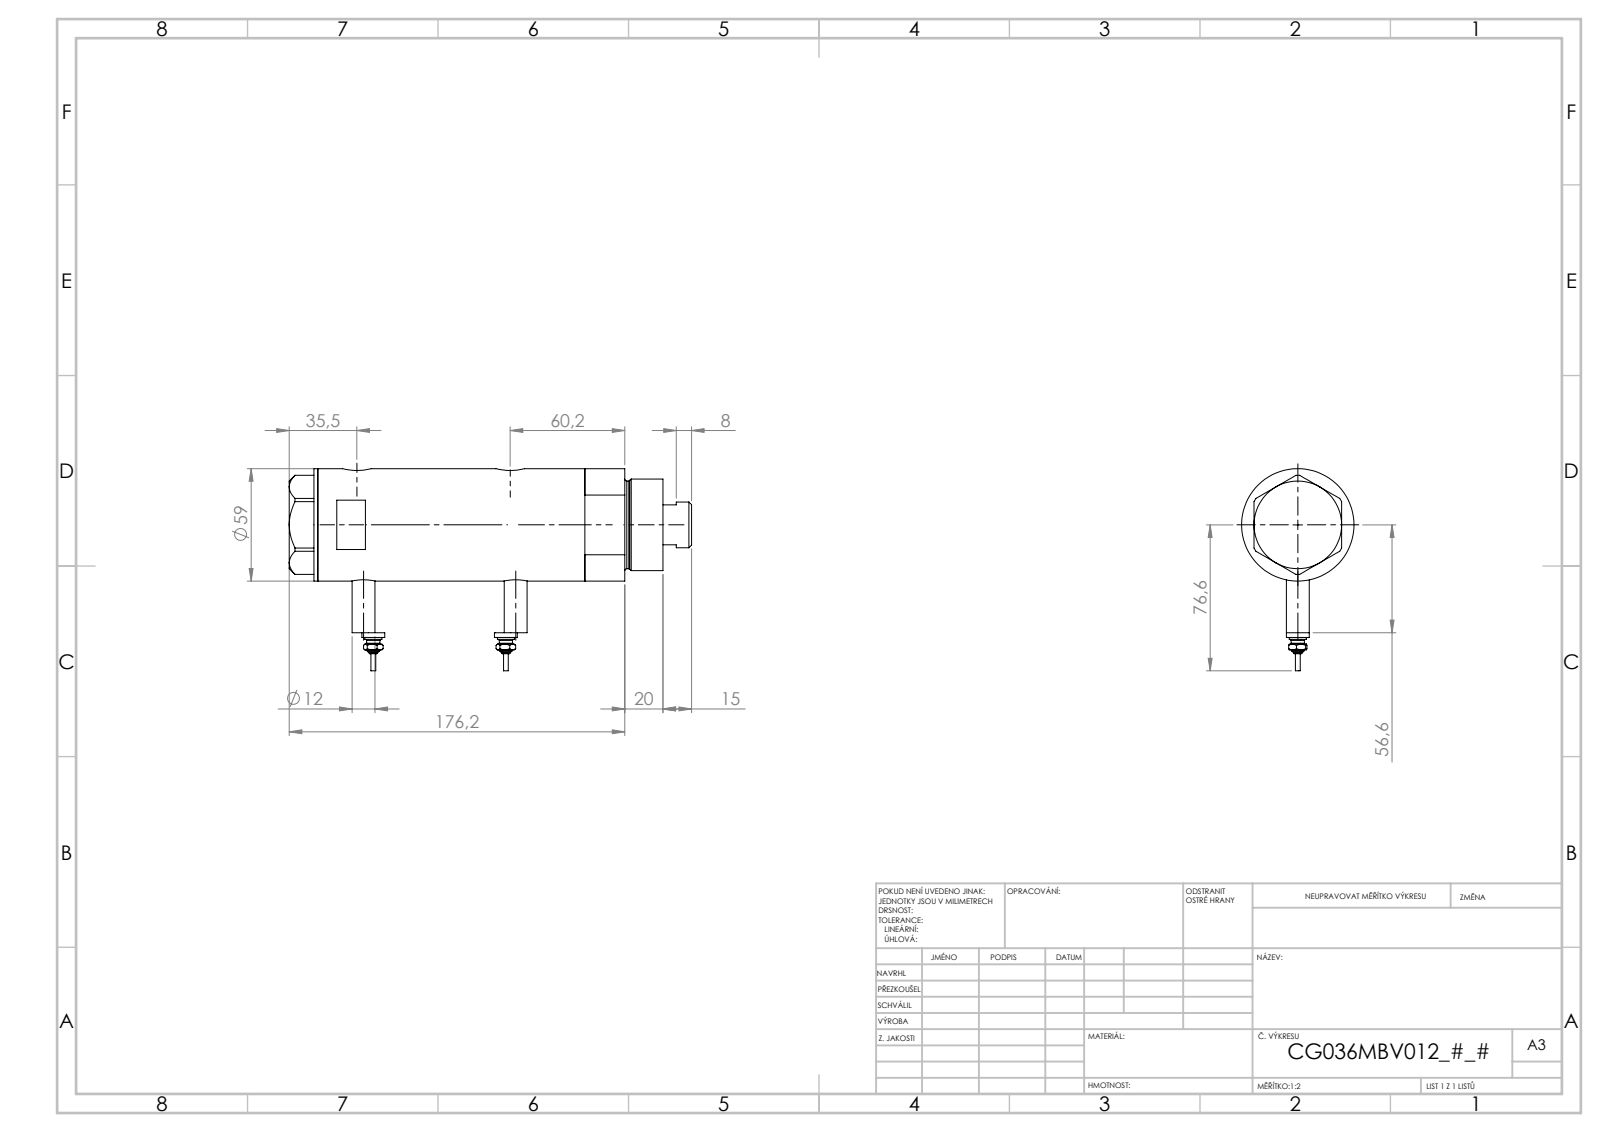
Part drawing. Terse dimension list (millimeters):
name: V270CG_VC; V270CG_FRONT; Switch; V270CG_MIDDLE (+1 more)
written by: SolidWorks 2019 (CONFIG_CONTROL_DESIGN)
unit: mm
bodies: 6 solids, 212 faces (79 planar, 69 cylindrical, 64 other)
size: 211.2 × 106.1 × 59
volume: 504 484 mm³; area: 104 067 mm²
holes: 2× ⌀9.73, 2× ⌀12.5, 2× ⌀15, 1× ⌀8.5, 1× ⌀25, 1× ⌀26.5, 1× ⌀36, 1× ⌀40, 1× ⌀52
bosses: 4× ⌀12, 2× ⌀9, 2× ⌀7, 2× ⌀4.5, 2× ⌀2.5, 1× ⌀59, 1× ⌀48, 1× ⌀46
face distances: 102.2, 23.5, 78.7, 15, 38.5, 117.2, 2, 196.2, 181.2, 50
hole spacings: 2.9, 3.5, 77, 79.9, 80.5, 83.4
